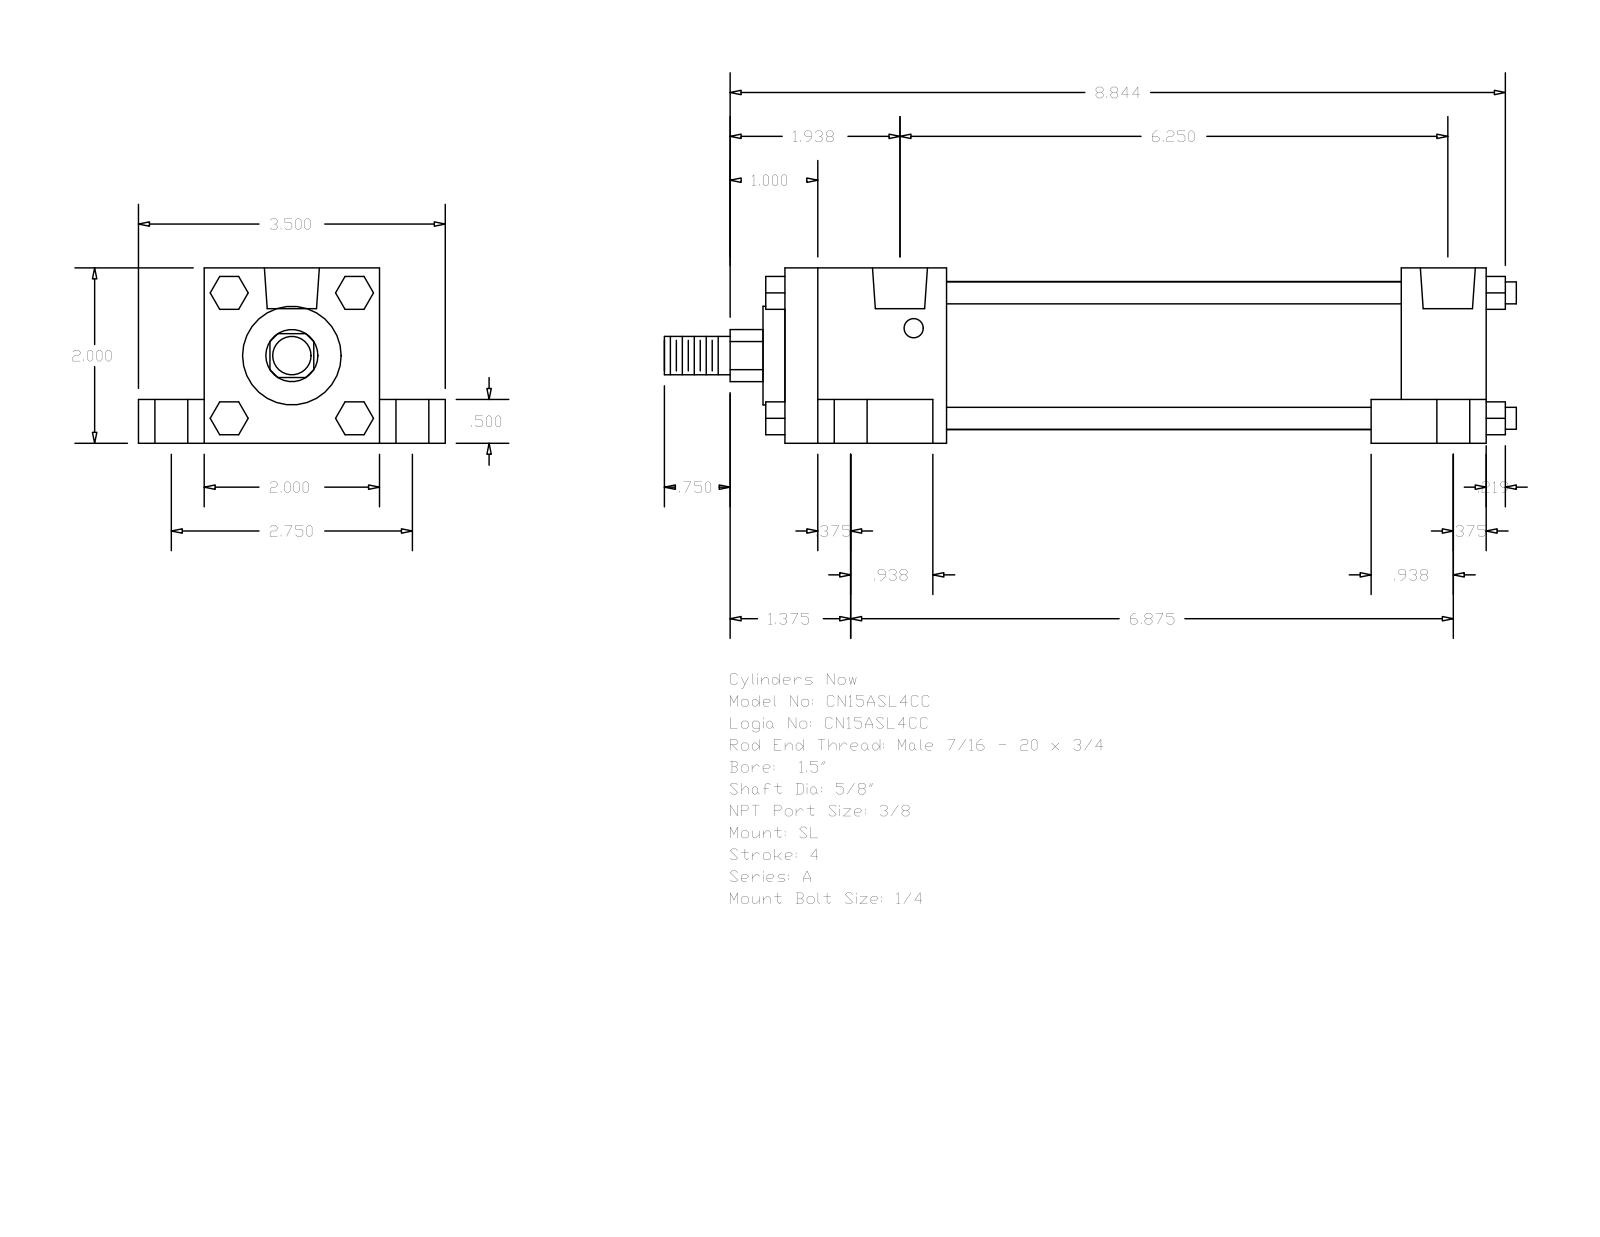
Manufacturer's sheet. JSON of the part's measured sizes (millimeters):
{"part_name": "A_SL__0150_0.625", "step_written_by": "GSSL Pune (CONFIG_CONTROL_DESIGN)", "units": "millimeters", "bodies": {"solids": 0, "faces": 148, "planar": 112, "cylindrical": 36, "other": 0}, "overall_size": [246.86, 88.9, 50.8], "round_holes": [[5.56, 4], [9.53, 4], [15.88, 4], [15.93, 2]], "round_bosses_or_shafts": [[6.35, 4], [42.93, 1], [28.57, 1], [15.88, 1], [11.11, 1]], "partial_cylinders_radius": [[7.54, 1]], "face_to_face_distances": [50.8, 19.05, 38.1, 12.7, 69.85, 203.19, 9.52, 178.59, 24.6, 46.83], "hole_center_spacings": [3.97, 34.96, 35.36, 37.73, 39.41, 69.84, 150.81, 154.78]}
